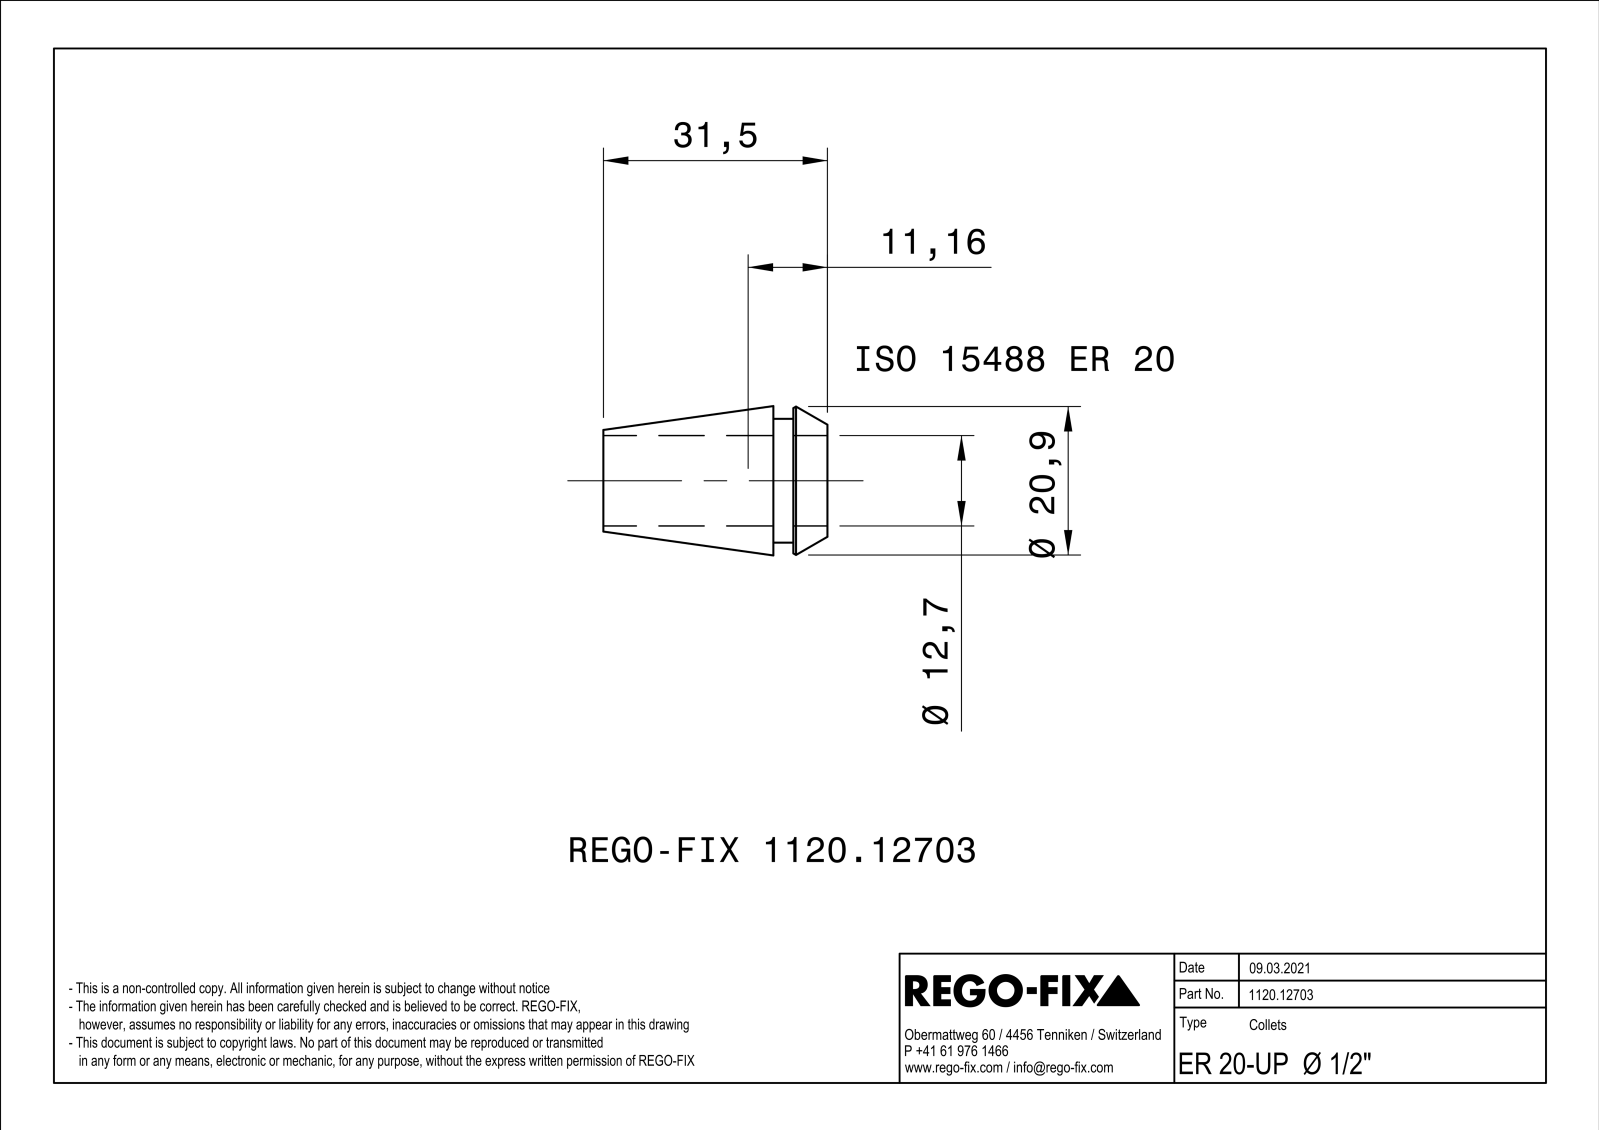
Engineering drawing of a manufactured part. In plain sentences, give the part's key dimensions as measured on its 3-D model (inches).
The part is named "NOCUT". Its 3-D file was written by "SIEMENS PLM Software Solid Edge ST10 (AUTOMOTIVE_DESIGN)". It is 1 solid with 177 faces: 88 planar, 9 cylindrical and 80 other. Overall it measures 1.24 by 0.826 by 0.826 inches. Its volume is 0.196 cubic inches and its surface area 7.838 square inches. Round holes: 1 of diameter 0.5. Round bosses or shafts: 1 of diameter 0.685. The main face-to-face distances are 0.024, 0.11, 0.189, 0.299, 1.24, 1.051, 0.941, 0.217, 0.028, 0.083.
